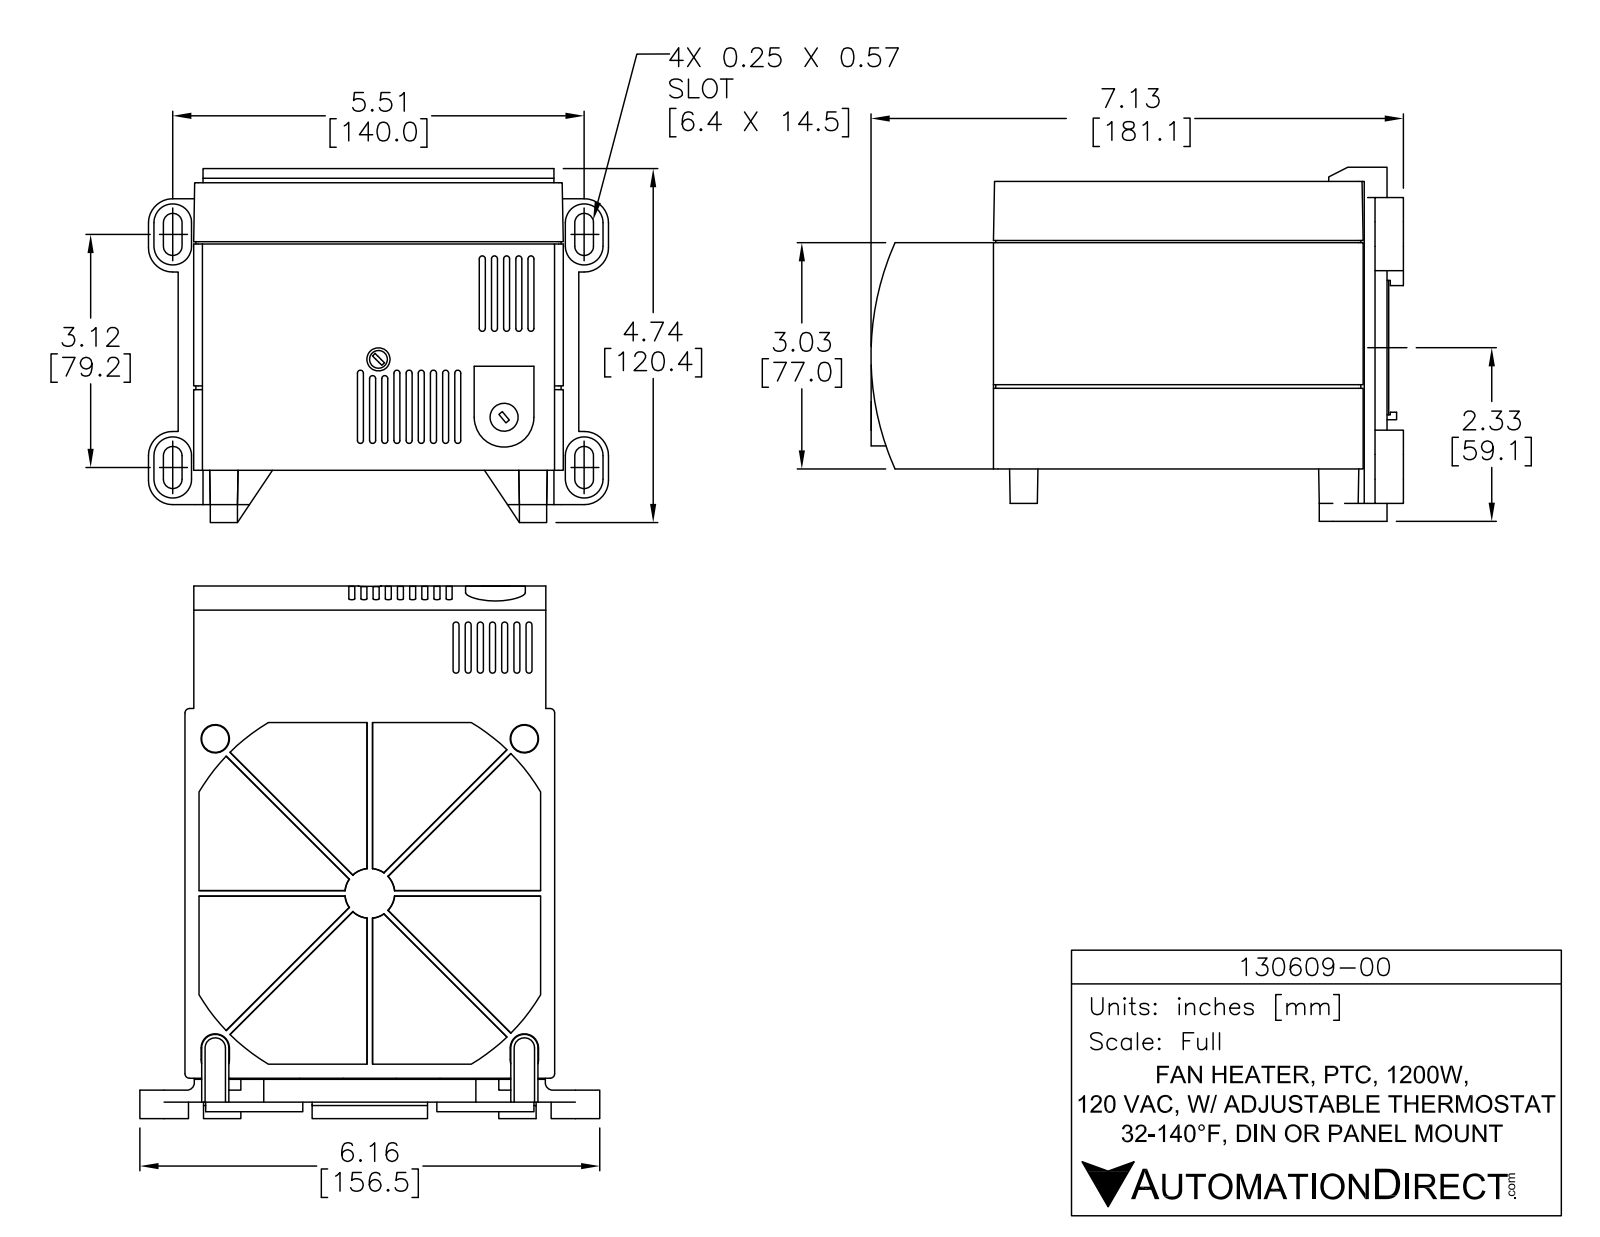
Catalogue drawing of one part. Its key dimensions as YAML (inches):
part_name: "130609-00"
step_written_by: "SolidWorks 2013 (AUTOMOTIVE_DESIGN)"
units: inches
bodies: {solids: 1, faces: 740, planar: 446, cylindrical: 257, other: 37}
overall_size: [7.13, 6.16, 4.74]
volume: 119.1
surface_area: 278.2
round_holes:
  - {diameter: 0.31, count: 1}
  - {diameter: 0.36, count: 1}
round_bosses_or_shafts:
  - {diameter: 0.375, count: 1}
  - {diameter: 0.238, count: 1}
partial_cylinders:
  - {radius: 0.07, count: 84}
  - {radius: 0.04, count: 42}
  - {radius: 0.325, count: 16}
  - {radius: 0.125, count: 8}
  - {radius: 0.252, count: 8}
  - {radius: 0.03, count: 4}
  - {radius: 0.06, count: 4}
  - {radius: 0.1, count: 2}
face_to_face_distances: [0.305, 0.015, 4.95, 0.32, 0.06, 0.22, 3.6, 3.54, 3.85, 3.79]
